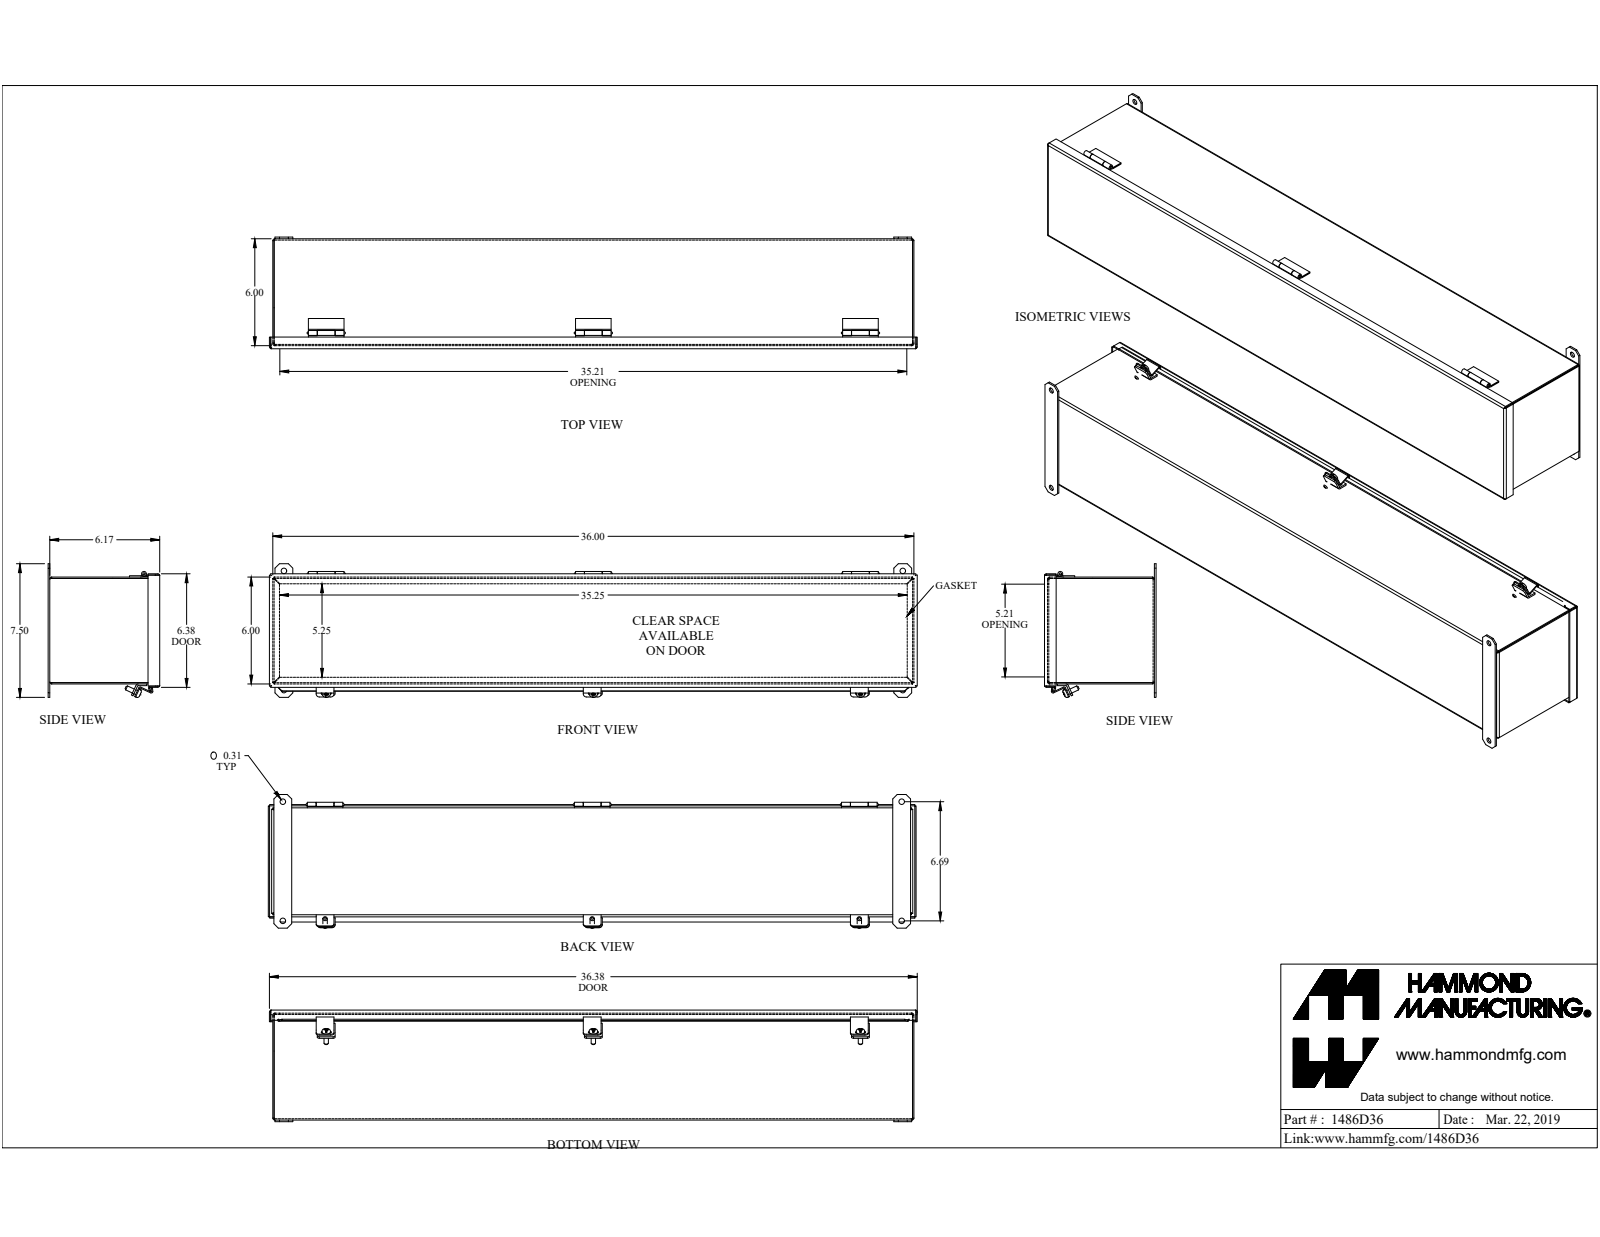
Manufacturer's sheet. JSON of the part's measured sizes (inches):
{"part_name": "1486D36", "step_written_by": "SolidWorks 2019 (CONFIG_CONTROL_DESIGN)", "units": "inches", "bodies": {"solids": 26, "faces": 536, "planar": 355, "cylindrical": 124, "other": 57}, "overall_size": [36.375, 7.506, 6.267], "volume_in3": 87.65, "surface_area_in2": 2283, "round_holes": [[0.313, 4], [0.213, 3], [0.125, 1]], "round_bosses_or_shafts": [[0.48, 3], [0.246, 3], [0.275, 1], [0.125, 1]], "partial_cylinders_radius": [[0.036, 13], [0.108, 13], [0.188, 12], [0.25, 12], [0.01, 6], [0.141, 6], [0.029, 2], [0.086, 2]], "face_to_face_distances": [0.072, 5.928, 6.1, 6, 5.856, 6.172, 6.028, 0.187, 0.259, 35.928], "hole_center_spacings": [6.688, 15, 30, 34.75, 34.75, 35.387, 35.388]}
